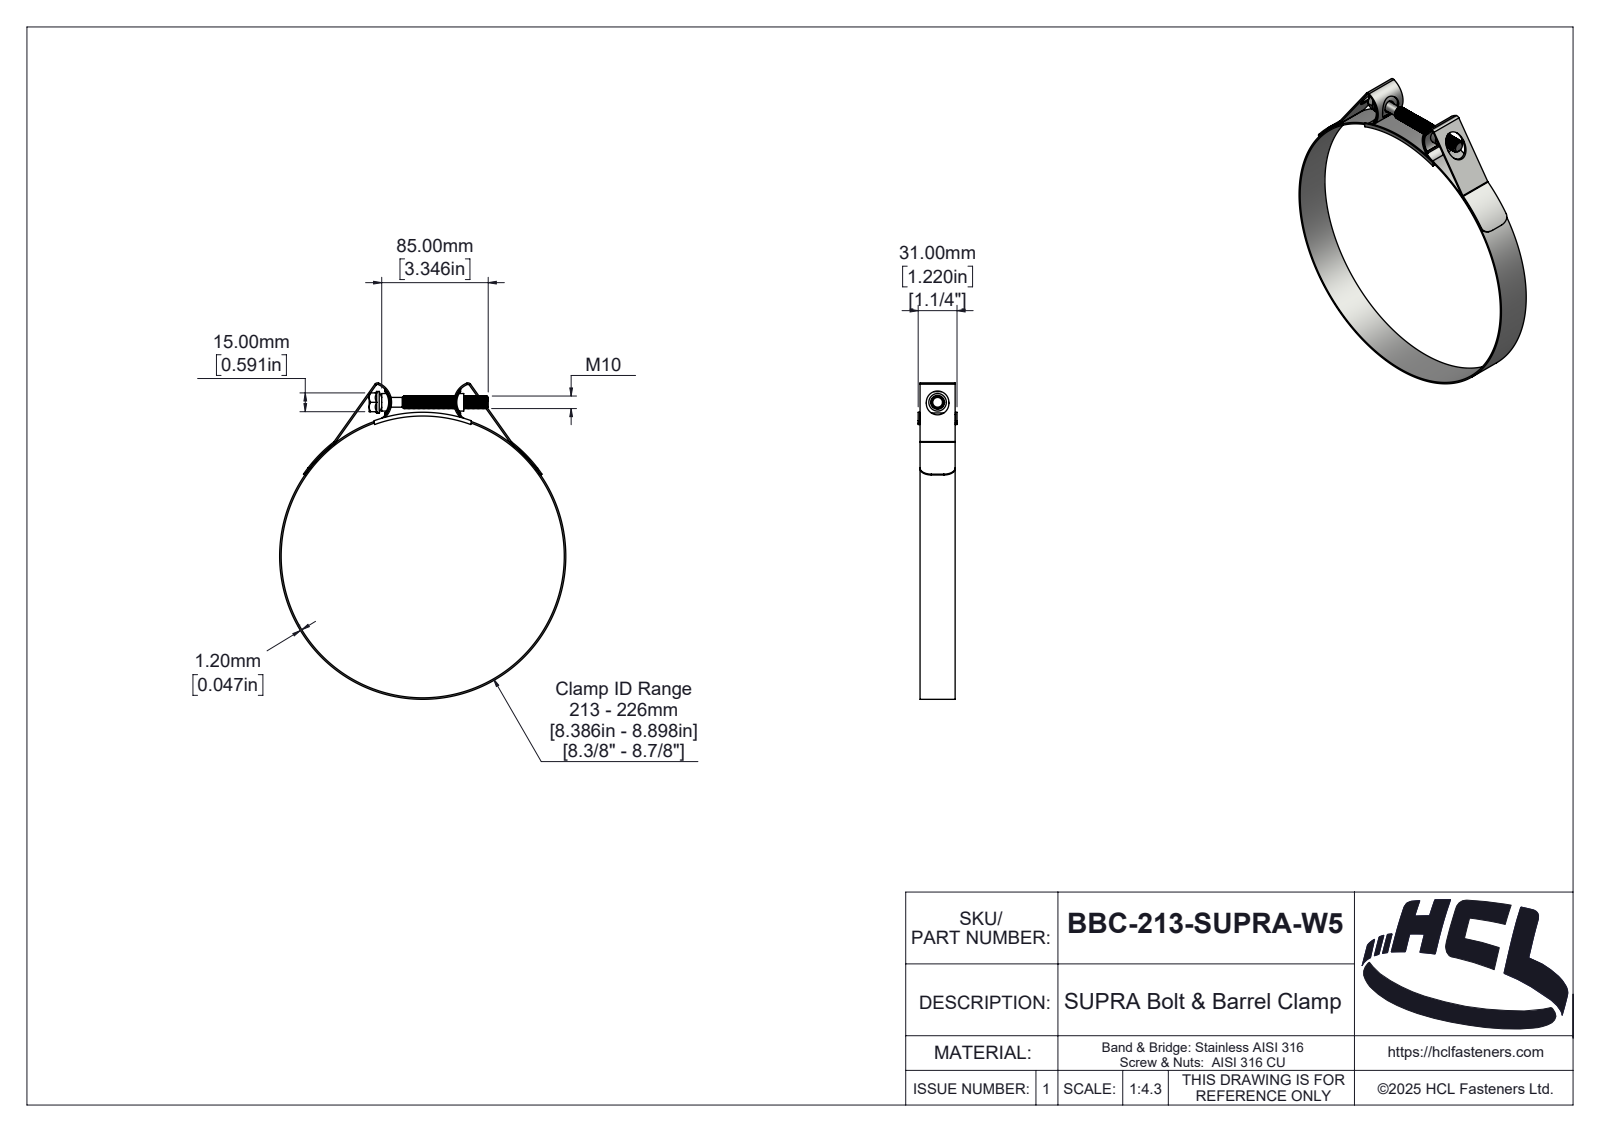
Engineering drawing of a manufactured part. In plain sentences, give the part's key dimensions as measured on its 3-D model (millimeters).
The part is named "BBC-213-SUPRA-W5". Its 3-D file was written by "SolidWorks 2025 (AUTOMOTIVE_DESIGN)". It is 5 solids with 383 faces: 50 planar, 246 cylindrical and 87 other. Overall it measures 252.44 by 228.4 by 31 millimeters. Its volume is 41 434 cubic millimeters and its surface area 64 078 square millimeters. Round holes: 1 of diameter 226. Round bosses or shafts: 1 of diameter 228.4, 1 of diameter 17.32, 1 of diameter 14, 1 of diameter 10, 1 of diameter 7.8. Partial cylindrical surfaces (rounded edges, fillets, slot ends): 4 of radius 1, 2 of radius 1.3, 2 of radius 2, 2 of radius 2.5, 2 of radius 3.2, 2 of radius 9, 2 of radius 14.24, 2 of radius 15.24. The main face-to-face distances are 1.2, 28, 1.5, 29.5, 29.8, 28.3, 31, 28.6, 15, 2.5.
